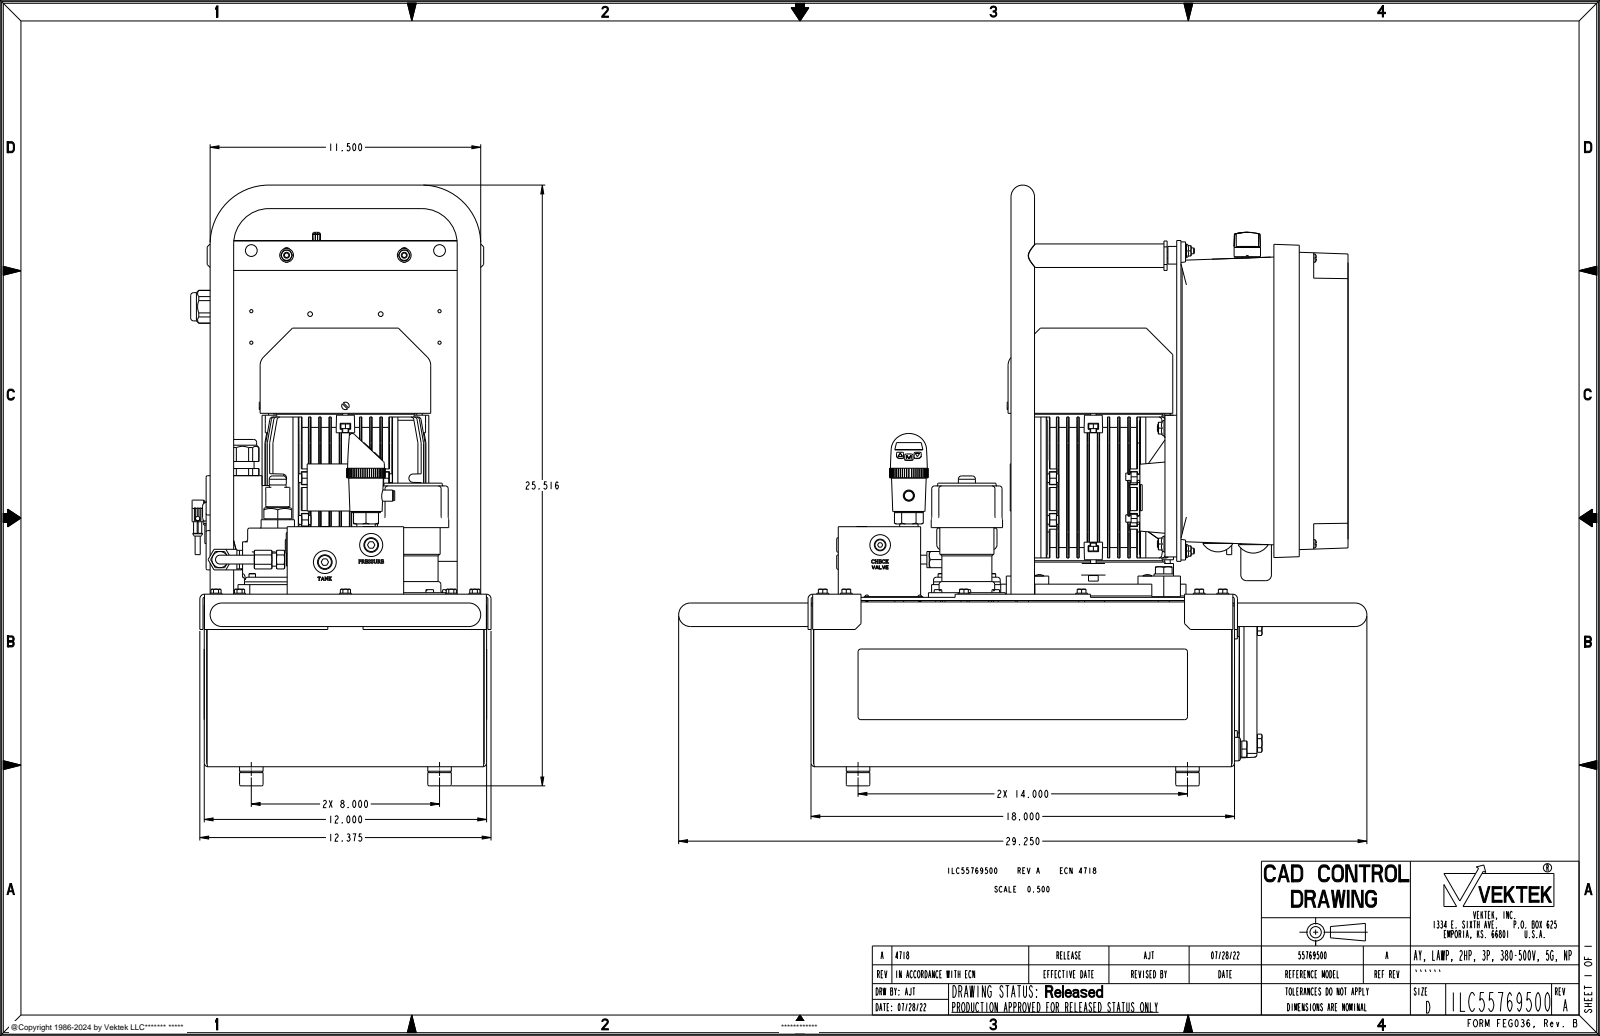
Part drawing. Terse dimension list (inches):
name: ILC55769500
written by: CREO PARAMETRIC BY PTC INC, 2021164 (AUTOMOTIVE_DESIGN)
unit: in
bodies: 10 solids, 9227 faces (4243 planar, 2490 cylindrical, 2494 other)
size: 29.25 × 25.516 × 12.764
volume: 786.5 in³; area: 5 193 in²
holes: 14× ⌀0.312, 14× ⌀0.344, 8× ⌀0.118, 8× ⌀0.75, 6× ⌀0.218, 6× ⌀0.354, 6× ⌀0.472, 6× ⌀0.5, 6× ⌀0.875, 5× ⌀0.079, 5× ⌀0.165, 5× ⌀0.236
bosses: 24× ⌀0.25, 14× ⌀1, 14× ⌀0.5, 9× ⌀0.375, 9× ⌀0.197, 9× ⌀0.177, 8× ⌀0.35, 7× ⌀0.472
rounds: 124× R0.118, 82× R0.02, 55× R0.039, 54× R0.005, 41× R0.079, 31× R0.157, 21× R0.197, 18× R0.108
face distances: 0.105, 0.138, 11.895, 7.06, 6.955, 17.895, 0.165, 0.135, 11.79, 6.992
hole spacings: 1.581, 14.867, 8, 4.2, 4.272, 4.5, 4.593, 5.335
